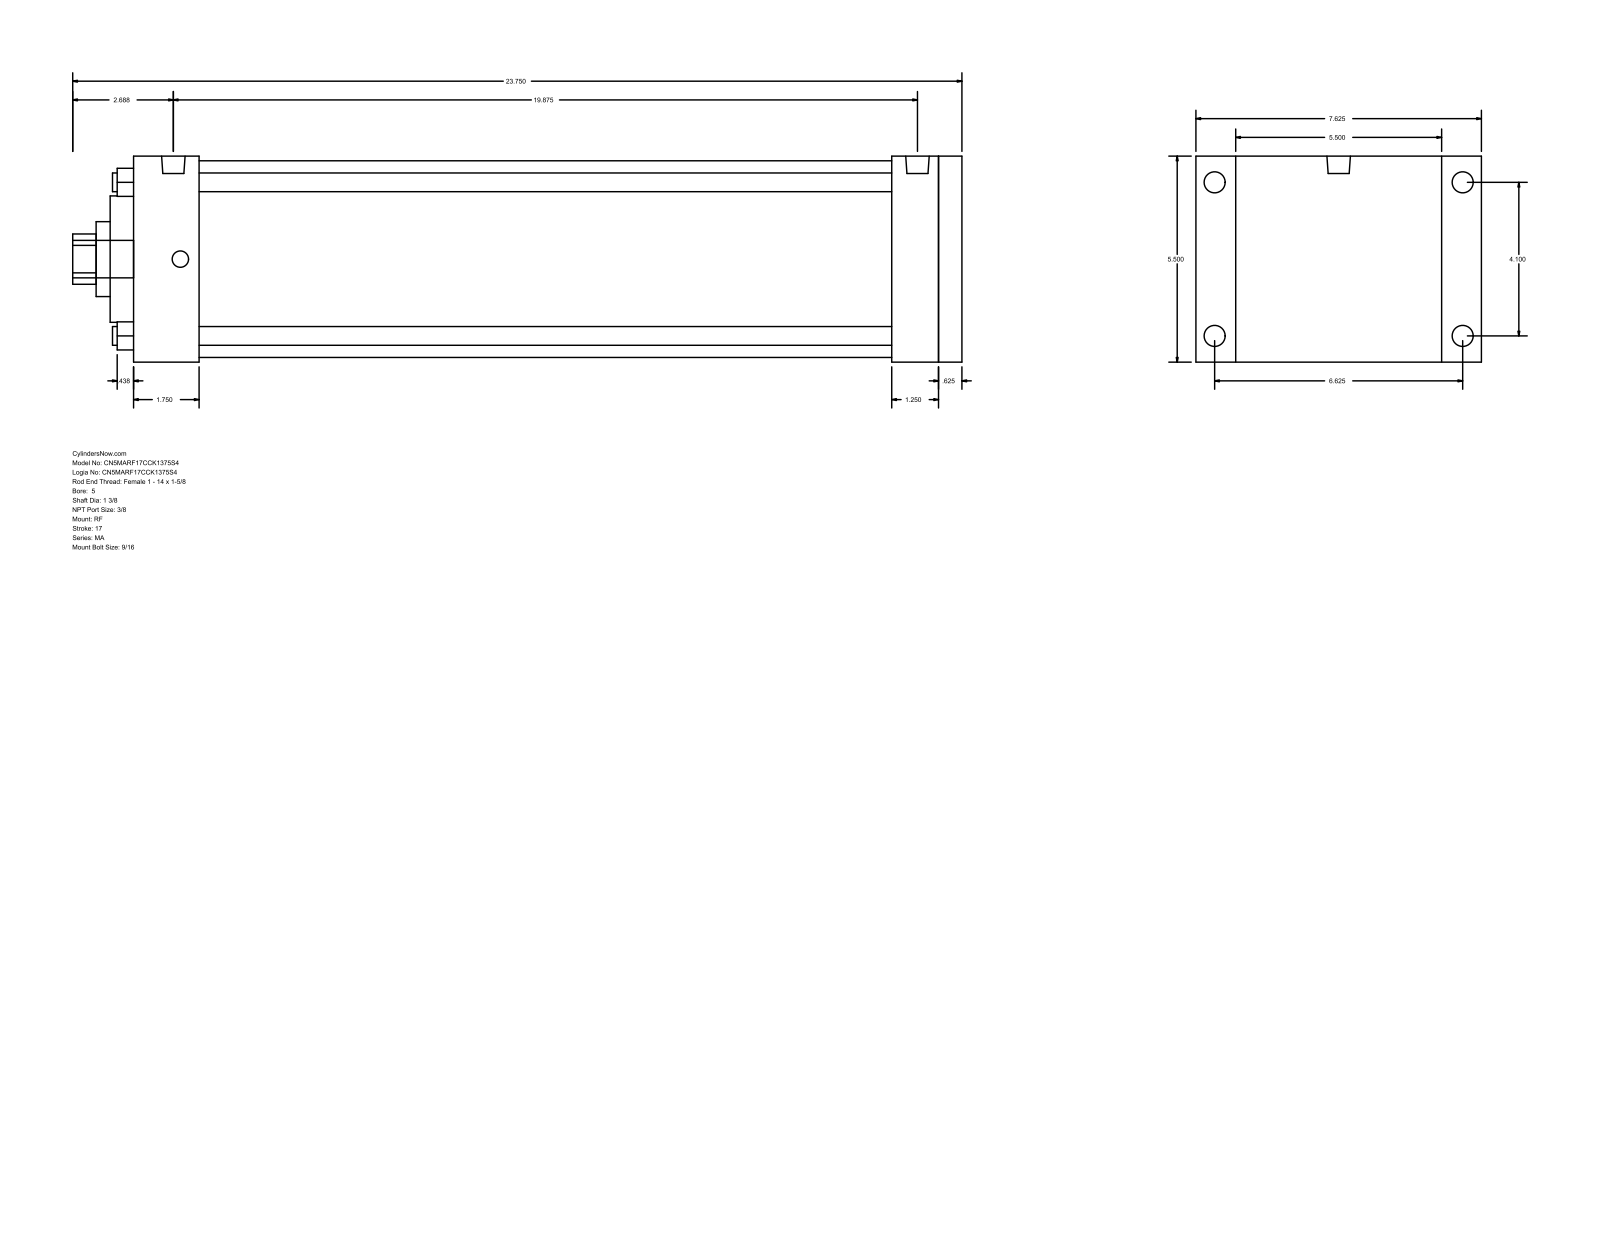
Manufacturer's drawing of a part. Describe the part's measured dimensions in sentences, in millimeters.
The part is named "MA_RF__0500_1.375". Its 3-D file was written by "GSSL Pune (CONFIG_CONTROL_DESIGN)". It is 0 solids with 94 faces: 65 planar, 29 cylindrical and 0 other. Overall it measures 603.25 by 193.68 by 139.7 millimeters. Round holes: 4 of diameter 12.7, 1 of diameter 34.92, 1 of diameter 50.8, 1 of diameter 85.72, 1 of diameter 133.35. Round bosses or shafts: 4 of diameter 14.29, 4 of diameter 11.11, 2 of diameter 15.93, 1 of diameter 25.4. Partial cylindrical surfaces (rounded edges, fillets, slot ends): 1 of radius 17.06. The main face-to-face distances are 139.7, 561.98, 15.87, 546.11, 44.45, 501.66, 517.53, 514.35, 469.9, 31.76. The hole center spacings are 73.64, 104.14, 147.28.
